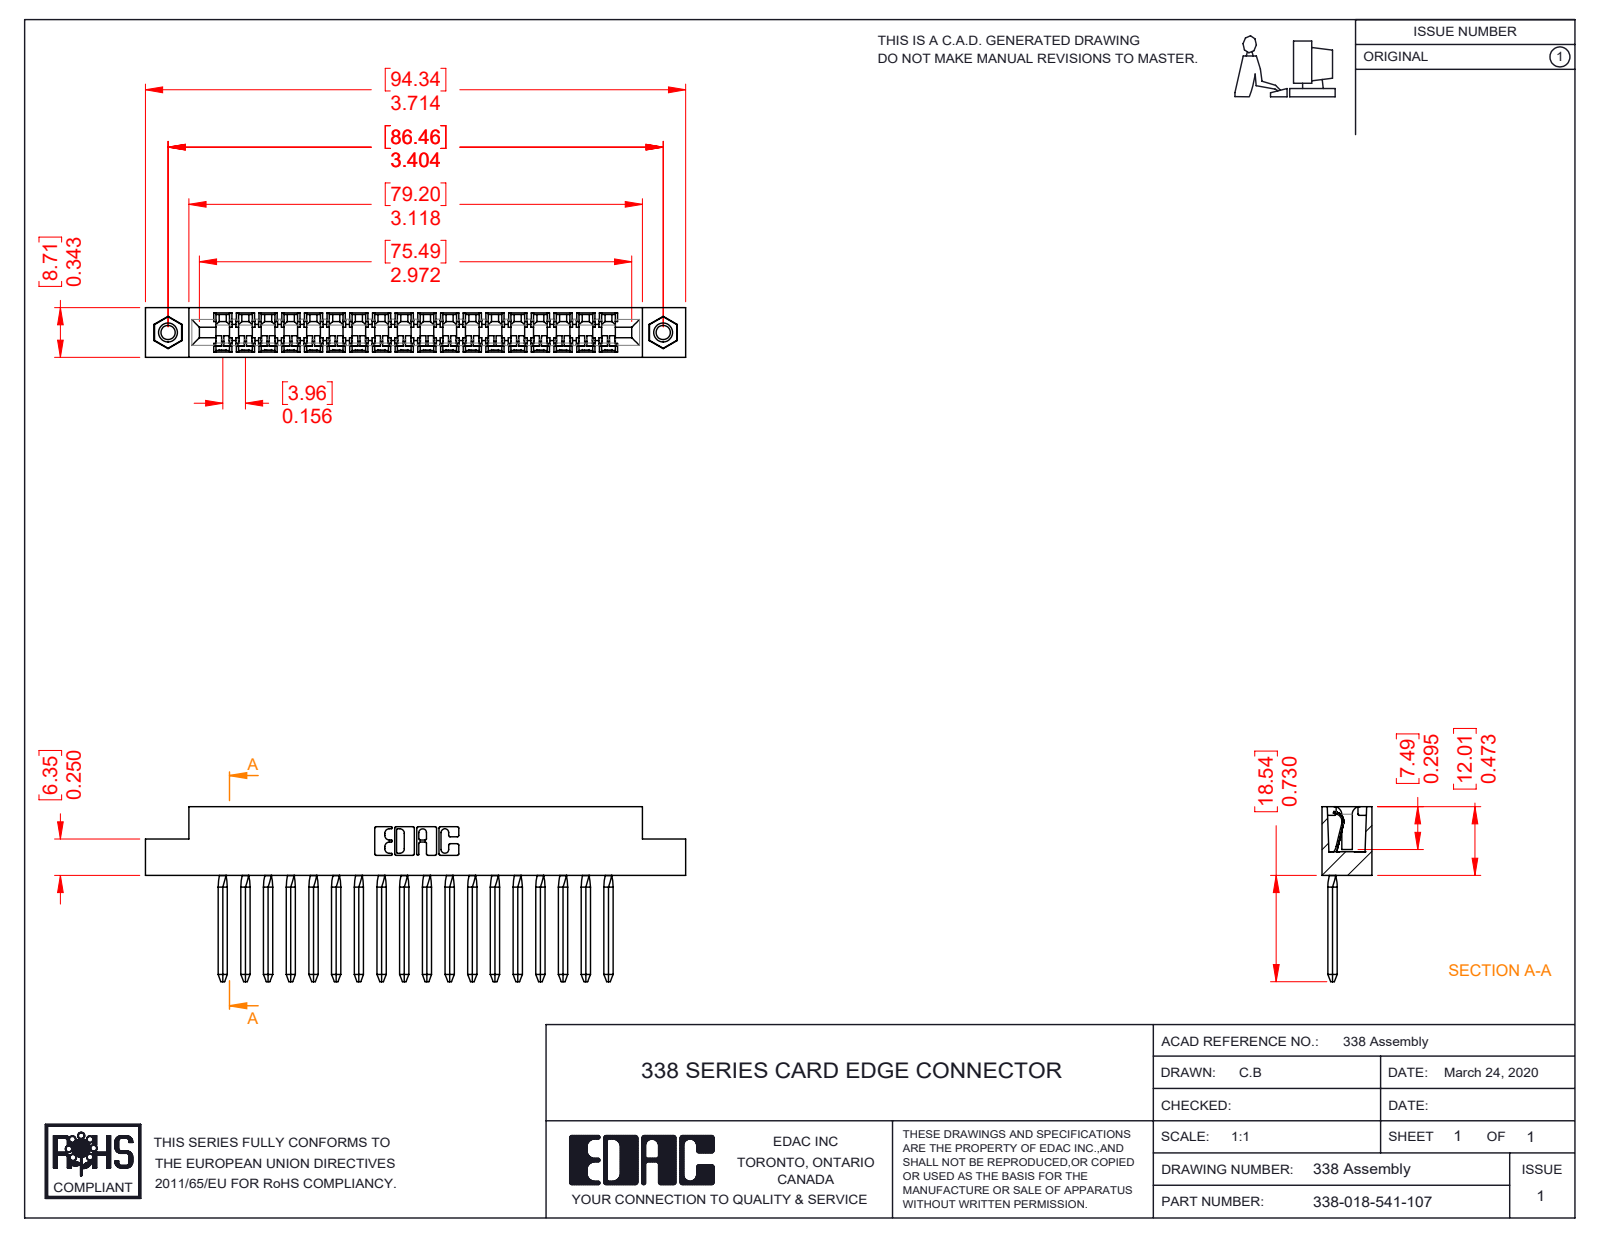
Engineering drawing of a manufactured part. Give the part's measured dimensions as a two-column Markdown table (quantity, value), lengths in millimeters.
| quantity | value |
| --- | --- |
| part name | 345-250-001_345-250-005-103; 338-018-541-107; 338-290-001_541; 338-210-001_338-210-018-004 |
| STEP written by | SolidWorks 2016 (CONFIG_CONTROL_DESIGN) |
| units | millimeters |
| bodies | 21 solids, 1828 faces (1252 planar, 488 cylindrical, 88 other) |
| overall size | 94.3 × 30.6 × 8.7 |
| volume | 6 570 mm³ |
| surface area | 10 450 mm² |
| round holes (diameter × count) | 2.5 × 2, 3.2 × 2, 4 × 2 |
| round bosses / shafts (diameter × count) | 3.9 × 2 |
| partial cylindrical surfaces (radius × count) | 0.6 × 74, 0.3 × 22, 0.2 × 18, 1.4 × 15, 1.7 × 15, 2.5 × 14, 0.2 × 6, 0.8 × 6 |
| main face-to-face distances | 8.7, 4, 15.8, 2.8, 19.8, 11.9, 5.3, 3.4, 5.6, 7.9 |
| hole center spacings | 86.5 |
